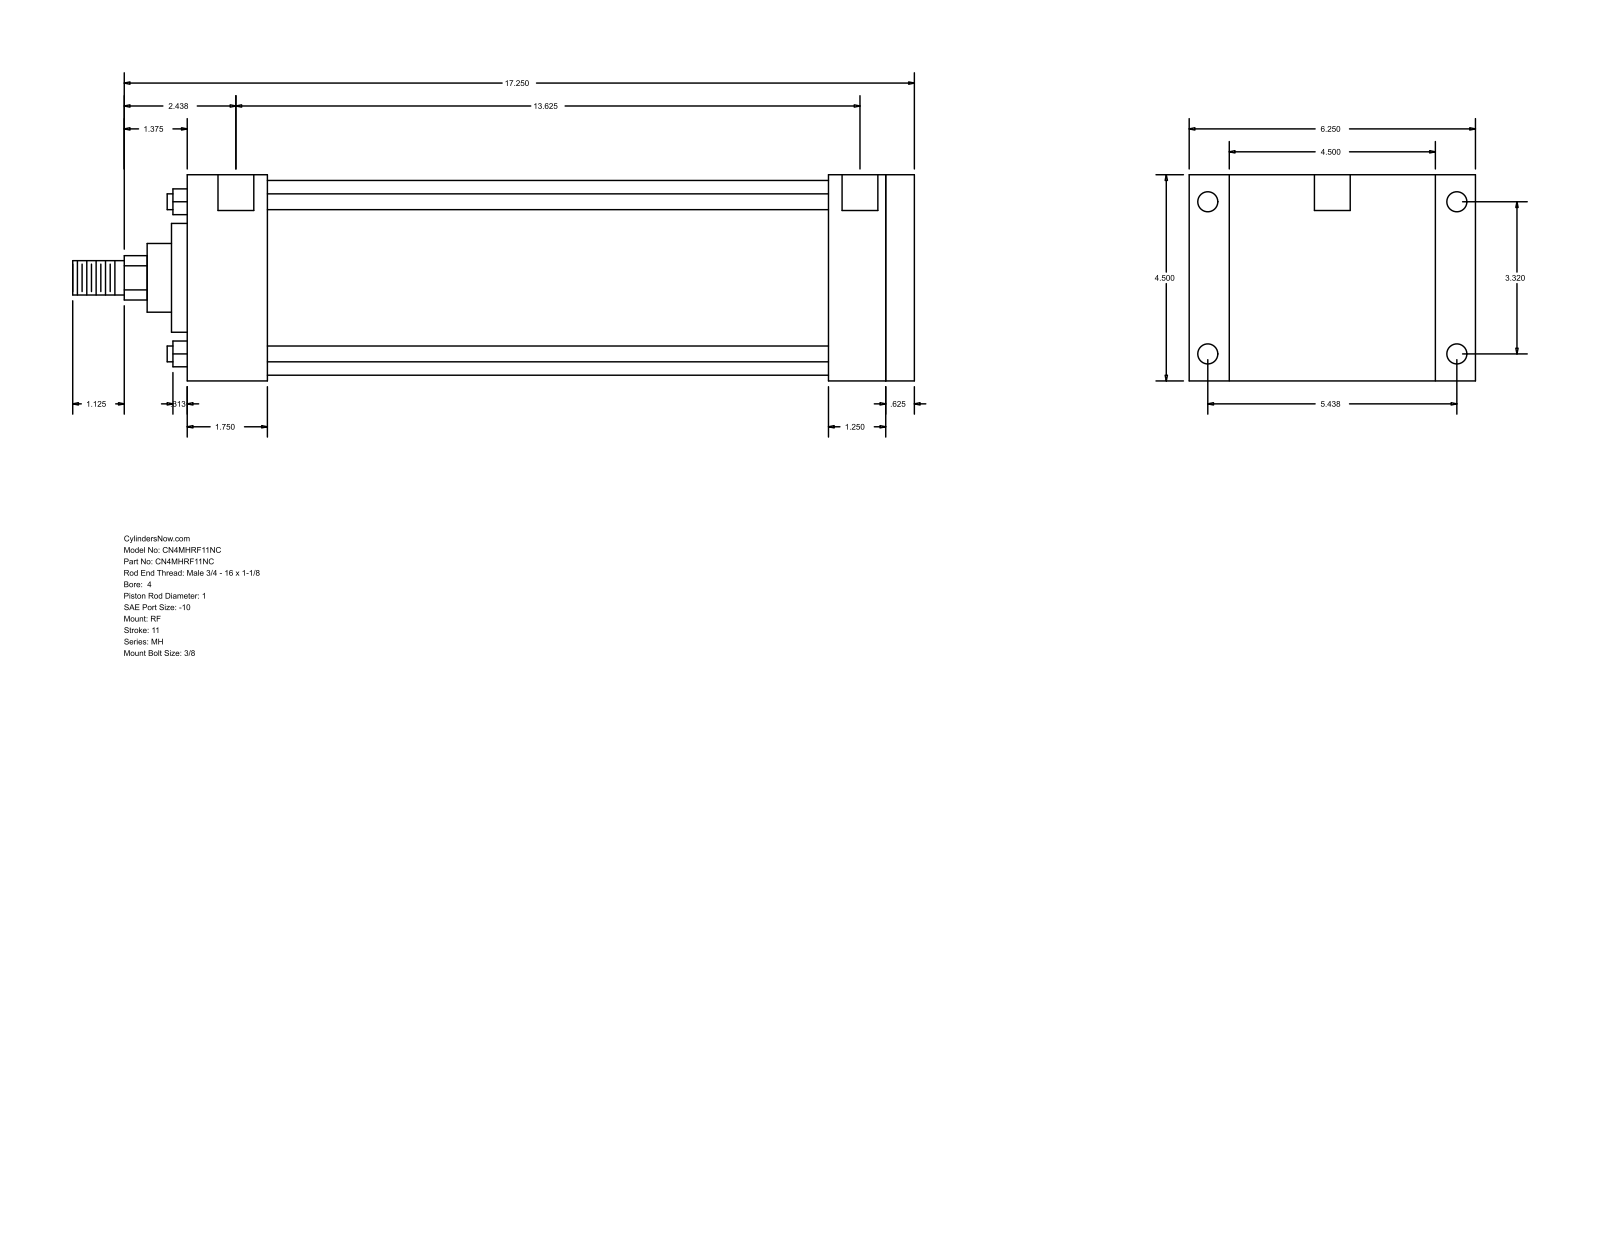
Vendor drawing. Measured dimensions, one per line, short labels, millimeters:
name: MH_RF__0400_1
written by: GSSL Pune (CONFIG_CONTROL_DESIGN)
unit: mm
bodies: 0 solids, 94 faces (65 planar, 29 cylindrical, 0 other)
size: 466.73 × 158.75 × 114.3
holes: 4× ⌀8.73, 4× ⌀11.13, 2× ⌀19.84
bosses: 4× ⌀8.76, 1× ⌀107.95, 1× ⌀60.33, 1× ⌀38.1, 1× ⌀25.4, 1× ⌀19.05
rounds: 1× R12.29
face distances: 114.3, 403.23, 387.35, 15.88, 47.63, 44.46, 342.89, 358.77, 355.6, 311.14
hole spacings: 1.58, 84.32, 138.12, 161.82, 347.66, 349.24, 346.08
